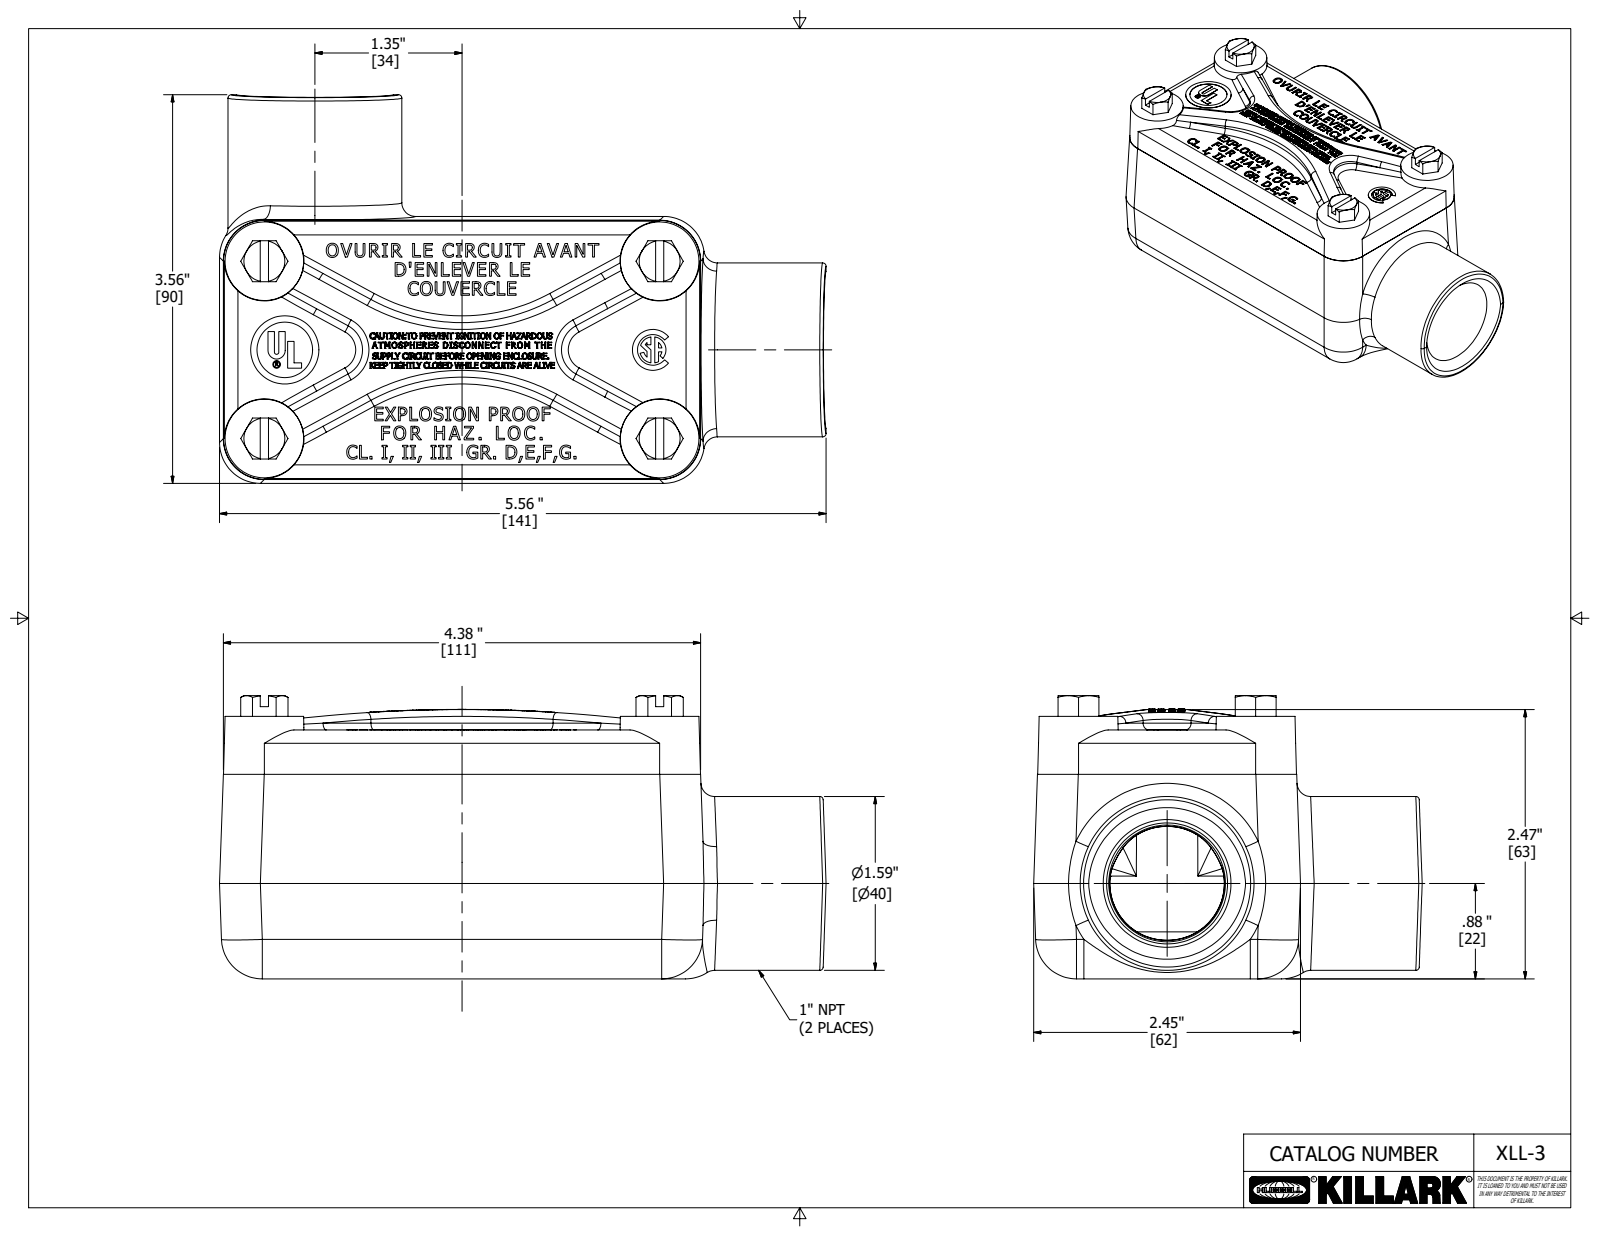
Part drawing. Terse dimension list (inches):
name: XLL-3; 0244484M; 0248904M; 0723660B
written by: Autodesk Inventor 2020 (AUTOMOTIVE_DESIGN)
unit: in
bodies: 6 solids, 5051 faces (2853 planar, 289 cylindrical, 1909 other)
size: 5.563 × 3.563 × 2.639
volume: 13.93 in³; area: 119.8 in²
holes: 4× ⌀0.196, 1× ⌀0.058, 1× ⌀0.509
bosses: 4× ⌀0.25, 2× ⌀1.594, 1× ⌀0.625, 1× ⌀0.069
rounds: 26× R0.125, 13× R0.187, 12× R0.062, 12× R0.375, 2× R0.25, 2× R0.75, 2× R1.75, 1× R0.007
face distances: 1.875, 2.281, 0.406, 0.27, 1.605, 2.011, 0.25, 0.203, 1.625, 0.203
hole spacings: 0.834, 1.625, 3.533, 3.625, 3.973, 0.153, 0.689, 0.952
